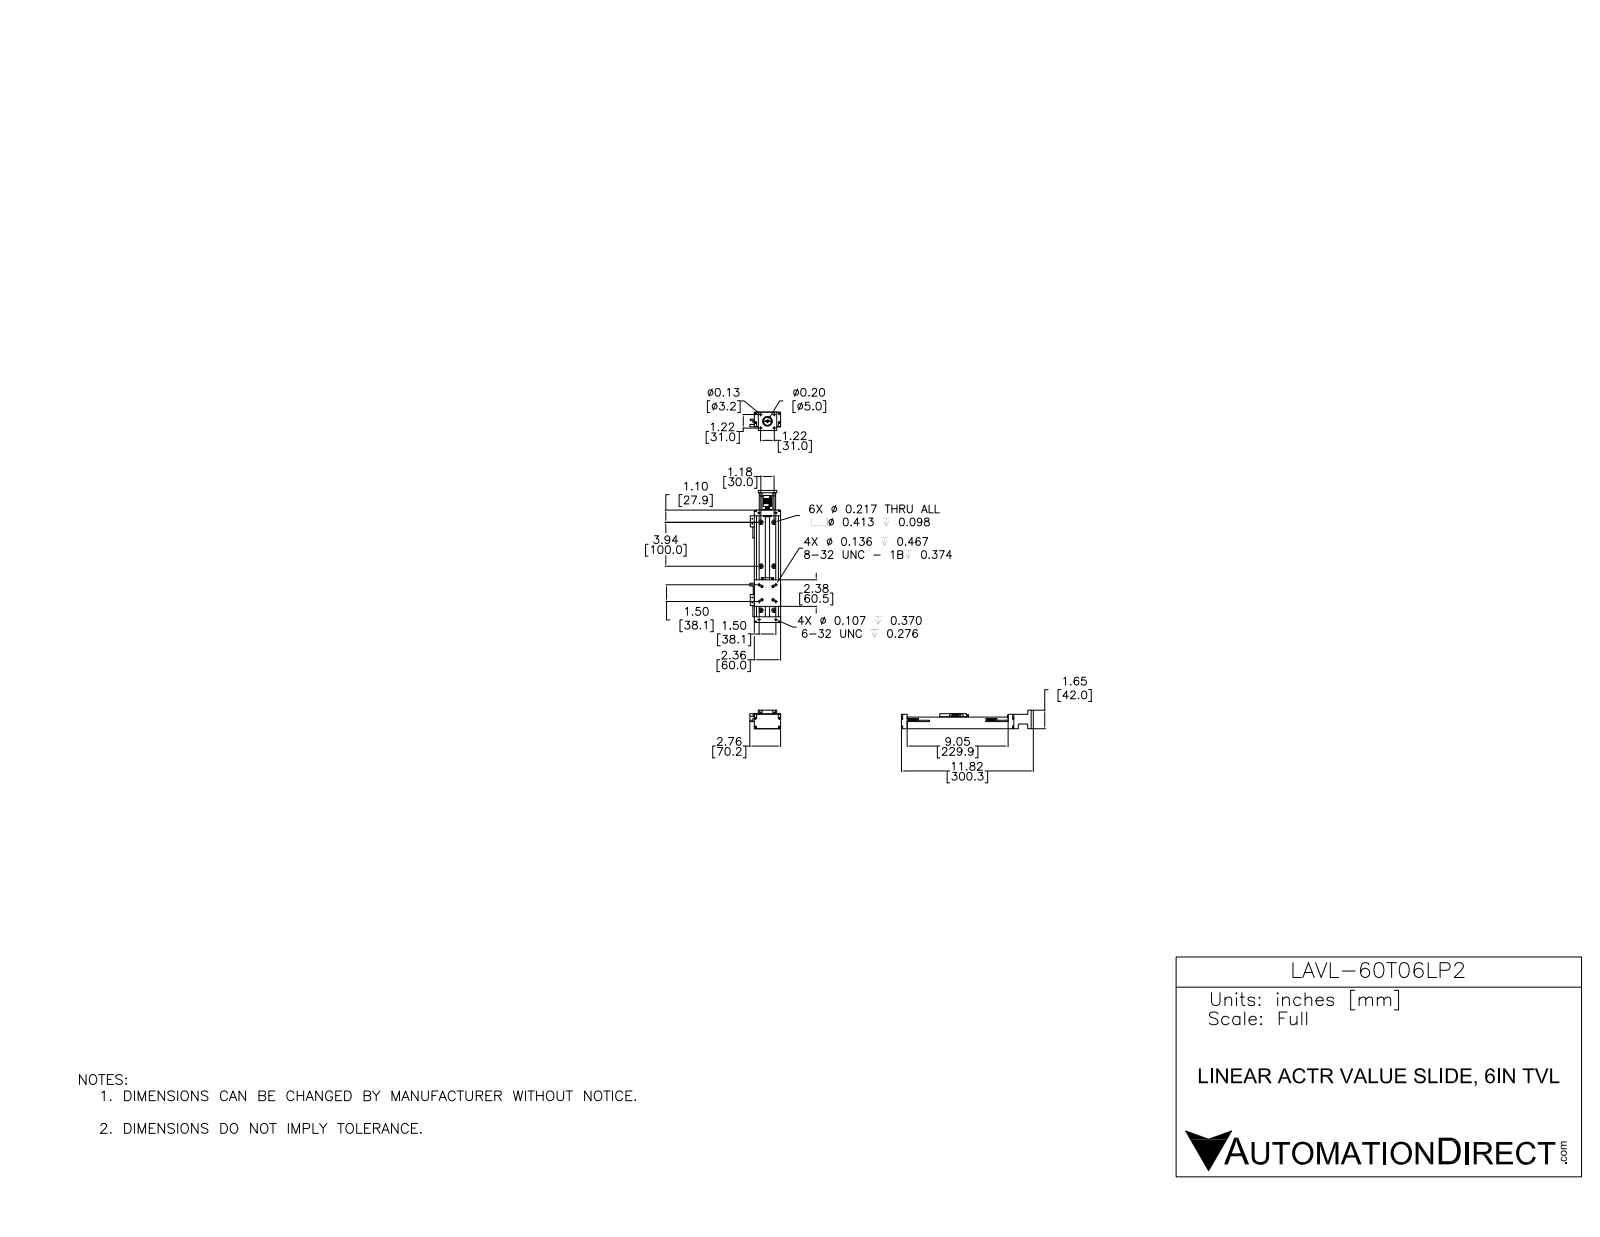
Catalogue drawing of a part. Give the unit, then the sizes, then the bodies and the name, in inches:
Units: inches
Overall size (bounding box): 11.824 × 2.762 × 1.654
Round holes (diameter × count): ⌀0.129 ×12, ⌀0.107 ×10, ⌀0.089 ×6, ⌀0.136 ×6, ⌀0.217 ×6, ⌀0.413 ×6, ⌀0.086 ×4, ⌀0.12 ×4, ⌀0.125 ×4, ⌀0.125 ×4, ⌀0.15 ×4, ⌀0.219 ×4
Round bosses / shafts (diameter × count): ⌀0.22 ×4, ⌀0.209 ×4, ⌀0.157 ×2, ⌀0.748 ×1, ⌀0.69 ×1, ⌀0.673 ×1, ⌀0.625 ×1, ⌀0.508 ×1
Partial cylindrical surfaces — rounded edges, fillets, slot ends (radius × count): R0.109 ×8, R0.047 ×4, R0.211 ×4, R0.266 ×4, R0.047 ×3, R0.188 ×3, R0.057 ×2, R0.062 ×2
Main face-to-face distances: 0.2, 2.162, 2.362, 1.962, 0.512, 9.562, 1.343, 1.143, 0.256, 0.25
Hole centre spacings: 1.089, 2.162, 1.22, 1.289, 1.5, 2.316, 0.292, 0.474
Volume: 17.92 in³ · Surface area: 216.4 in²
Bodies: 19 solids, 877 faces (330 planar, 376 cylindrical, 171 other)
Part name (STEP PRODUCT): LAVL-60T06LP2-RAIL; LAVL-60T06LP2; LAVL-60T06LP2-CAR
STEP written by: SolidWorks 2015 (AUTOMOTIVE_DESIGN)
